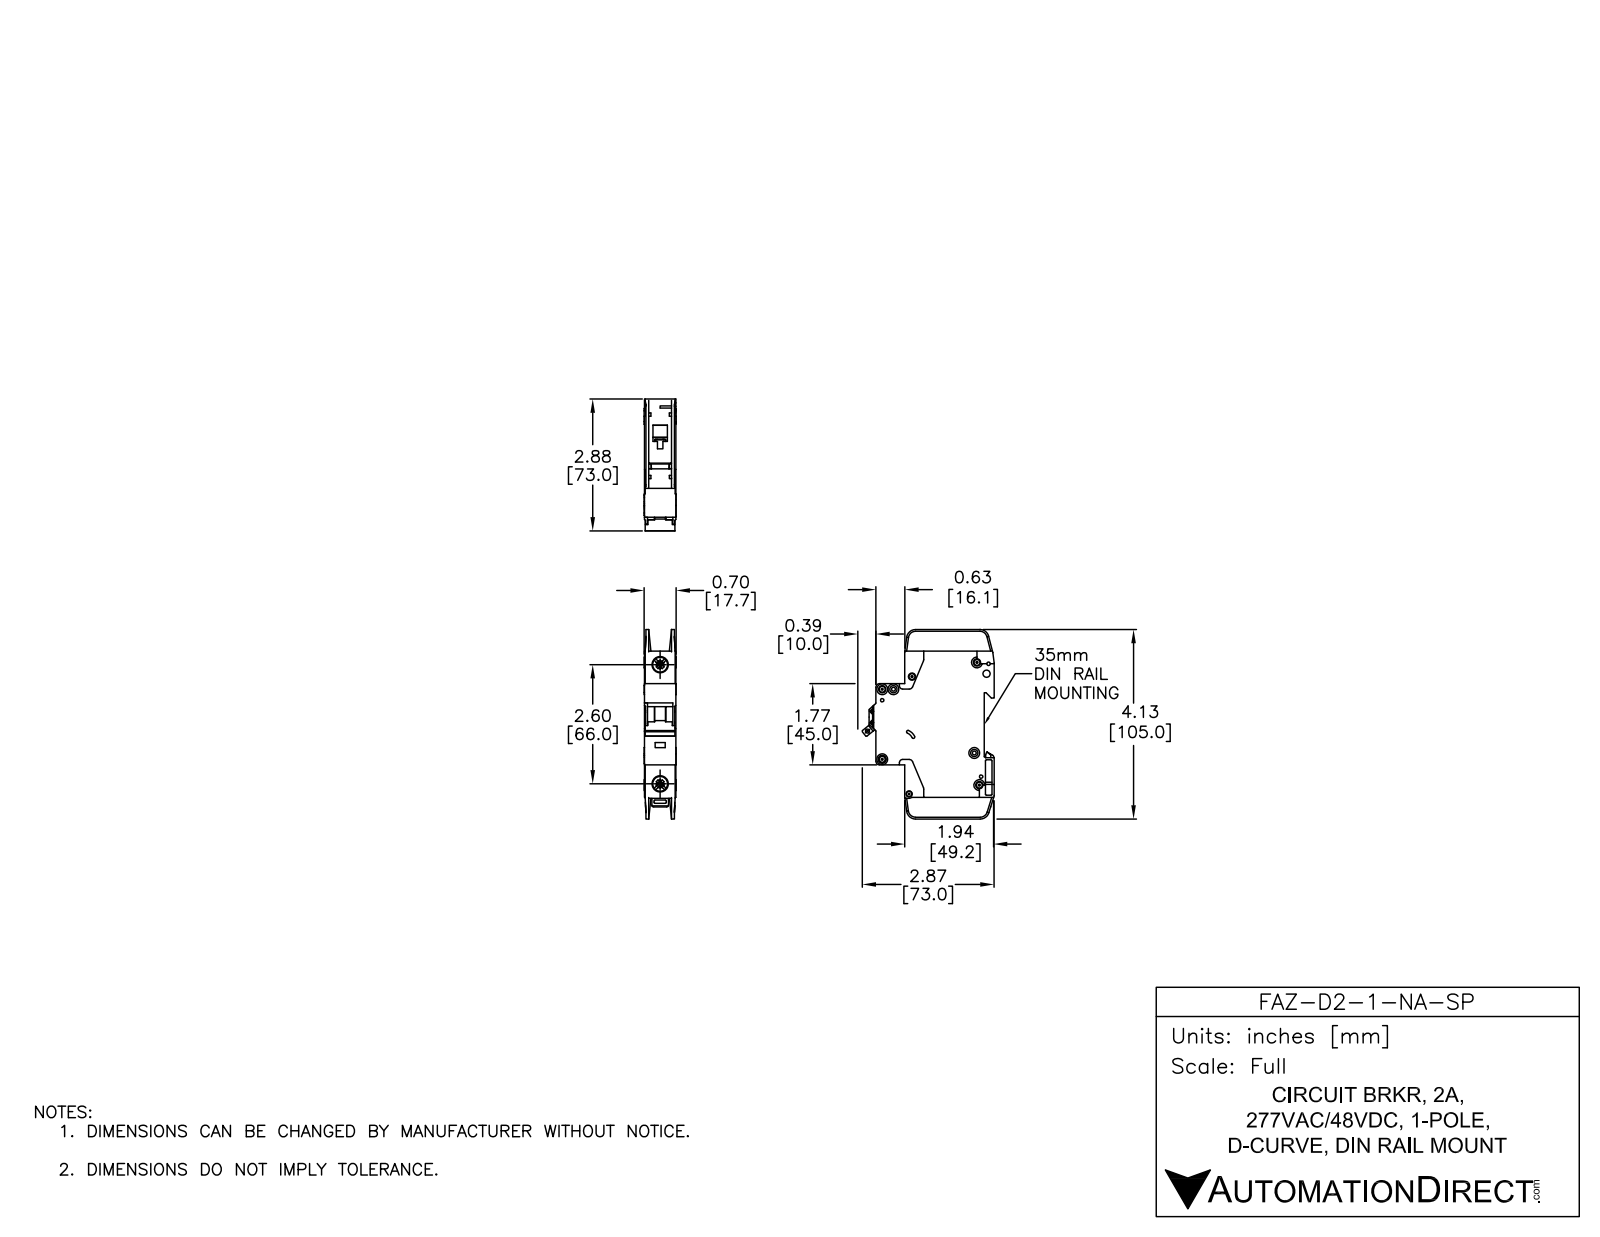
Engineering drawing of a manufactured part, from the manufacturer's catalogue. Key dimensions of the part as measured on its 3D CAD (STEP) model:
Part name (STEP PRODUCT): FAZ-D2-1-NA-SP
STEP written by: SolidWorks 2014 (AUTOMOTIVE_DESIGN)
Units: millimetres
Bodies: 3 solids, 784 faces (409 planar, 263 cylindrical, 112 other)
Overall size (bounding box): 105 × 73.04 × 17.7
Volume: 77 695 mm³ · Surface area: 24 740 mm²
Round holes (diameter × count): ⌀3.6 ×7, ⌀1.09 ×2, ⌀1.5 ×2, ⌀4 ×2, ⌀7.15 ×2, ⌀8.2 ×2, ⌀1.9 ×1, ⌀2.15 ×1, ⌀2.2 ×1, ⌀2.55 ×1, ⌀3.3 ×1, ⌀3.4 ×1
Round bosses / shafts (diameter × count): ⌀6 ×7, ⌀2.5 ×1
Partial cylindrical surfaces — rounded edges, fillets, slot ends (radius × count): R0.25 ×29, R0.5 ×18, R1 ×10, R2 ×10, R5 ×5, R4 ×4, R1.8 ×3, R0.2 ×2
Main face-to-face distances: 17.5, 15.05, 0.7, 2.45, 1.75, 15.75, 13.3, 14, 12.6, 2
Hole centre spacings: 6.2, 5.19, 6.1, 8.19, 8.56, 8.7, 11.11, 12.45
